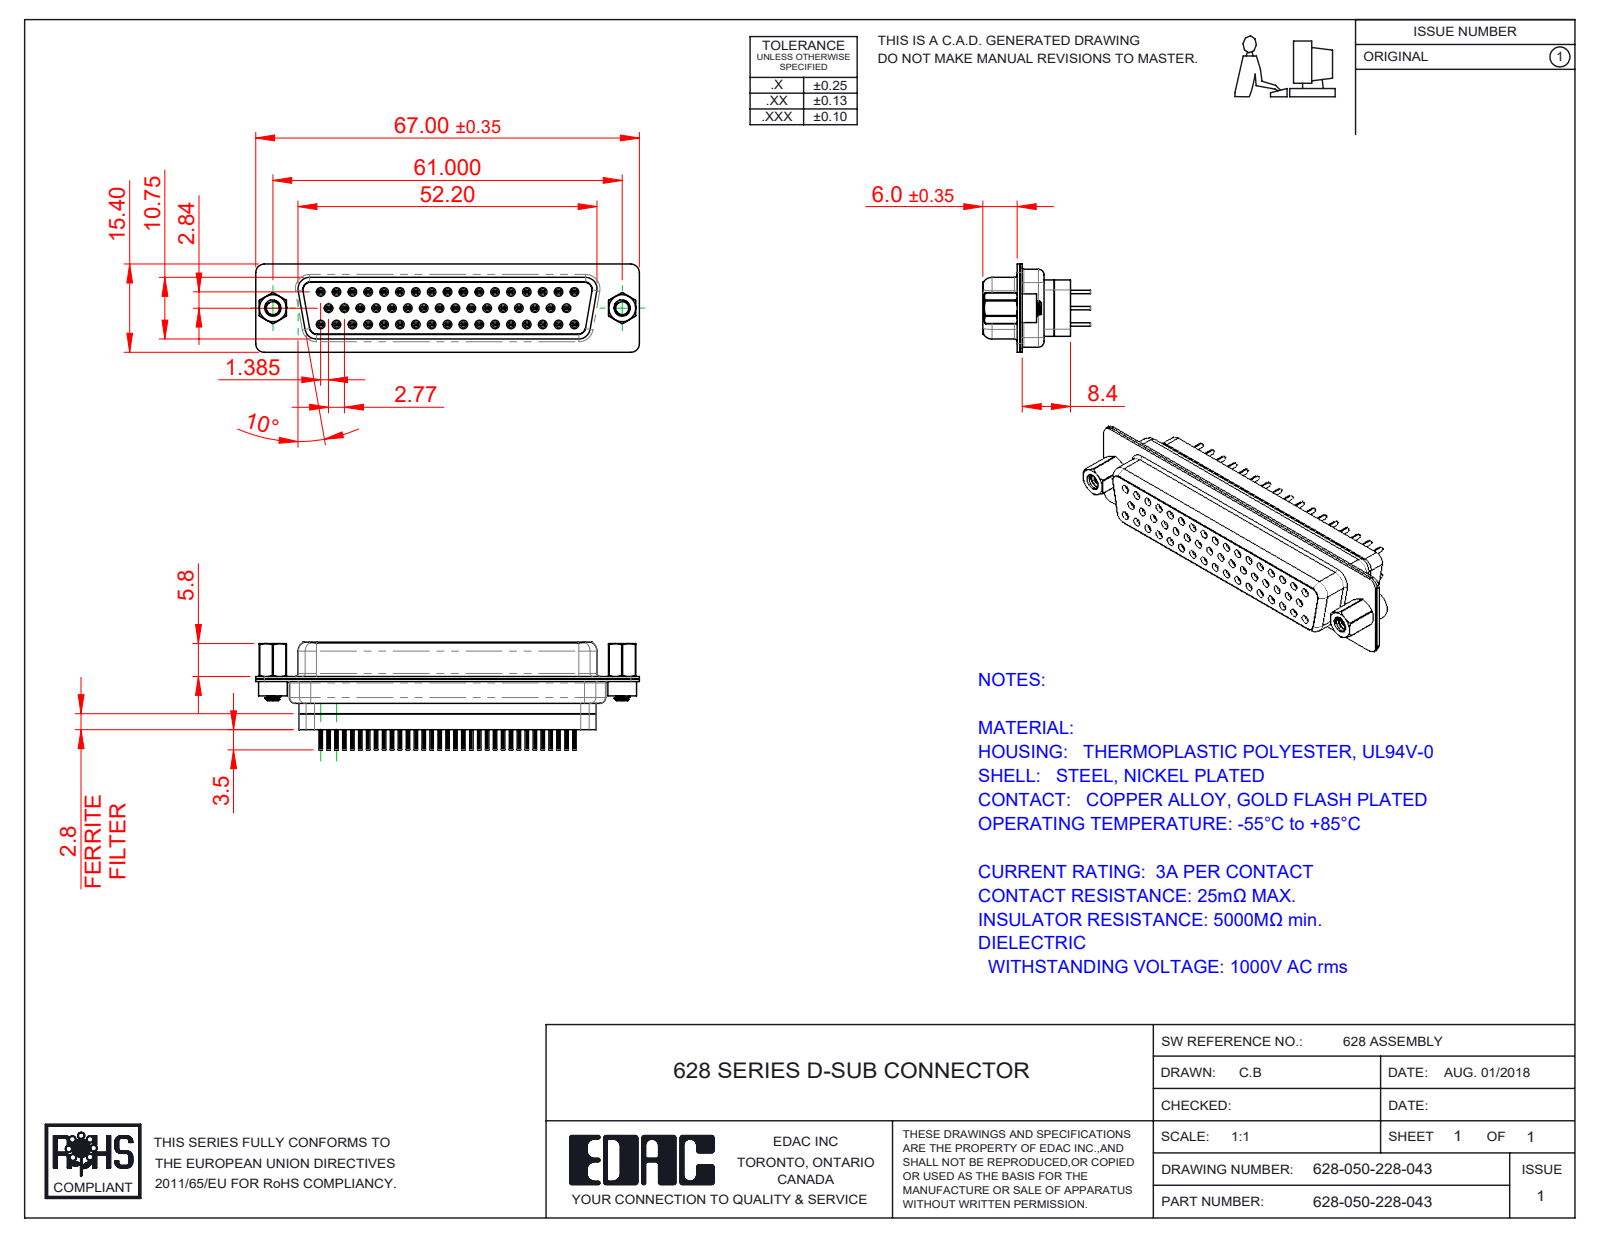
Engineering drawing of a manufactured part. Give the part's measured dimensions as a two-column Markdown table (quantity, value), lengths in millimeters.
| quantity | value |
| --- | --- |
| part name | 628 4-40 Threaded Rivet; 628 Shell Rear_50 Contacts; 628 Contact Row 1_28L; 628 4-40 Hex Standoff (+5 more) |
| STEP written by | SolidWorks 2020 (CONFIG_CONTROL_DESIGN) |
| units | millimeters |
| bodies | 58 solids, 6862 faces (1645 planar, 1962 cylindrical, 3255 other) |
| overall size | 67 × 18.8 × 15.4 |
| volume | 8 056 mm³ |
| surface area | 17 903 mm² |
| round holes (diameter × count) | 0.2 × 50, 0.8 × 50, 0.9 × 50, 1.1 × 50, 1.6 × 50, 1.7 × 17, 2.26 × 2, 2.29 × 2, 4 × 2, 4.05 × 2, 4.85 × 2 |
| round bosses / shafts (diameter × count) | 2 × 50, 1.5 × 50, 1.2 × 50, 0.6 × 50, 5 × 2, 4.95 × 2, 4.8 × 2, 2.79 × 2 |
| partial cylindrical surfaces (radius × count) | 0.1 × 100, 0.28 × 33, 1.5 × 16, 2 × 12, 1.35 × 8, 0.25 × 4, 0.5 × 4, 0.6 × 4 |
| main face-to-face distances | 0.45, 0.4, 6.05, 1.87, 11.33, 9.3, 9.85, 0.9, 6.5, 10.3 |
| hole center spacings | 2.77, 3.16, 5.54, 8.31, 11.08, 13.85, 16.62, 19.39 |
